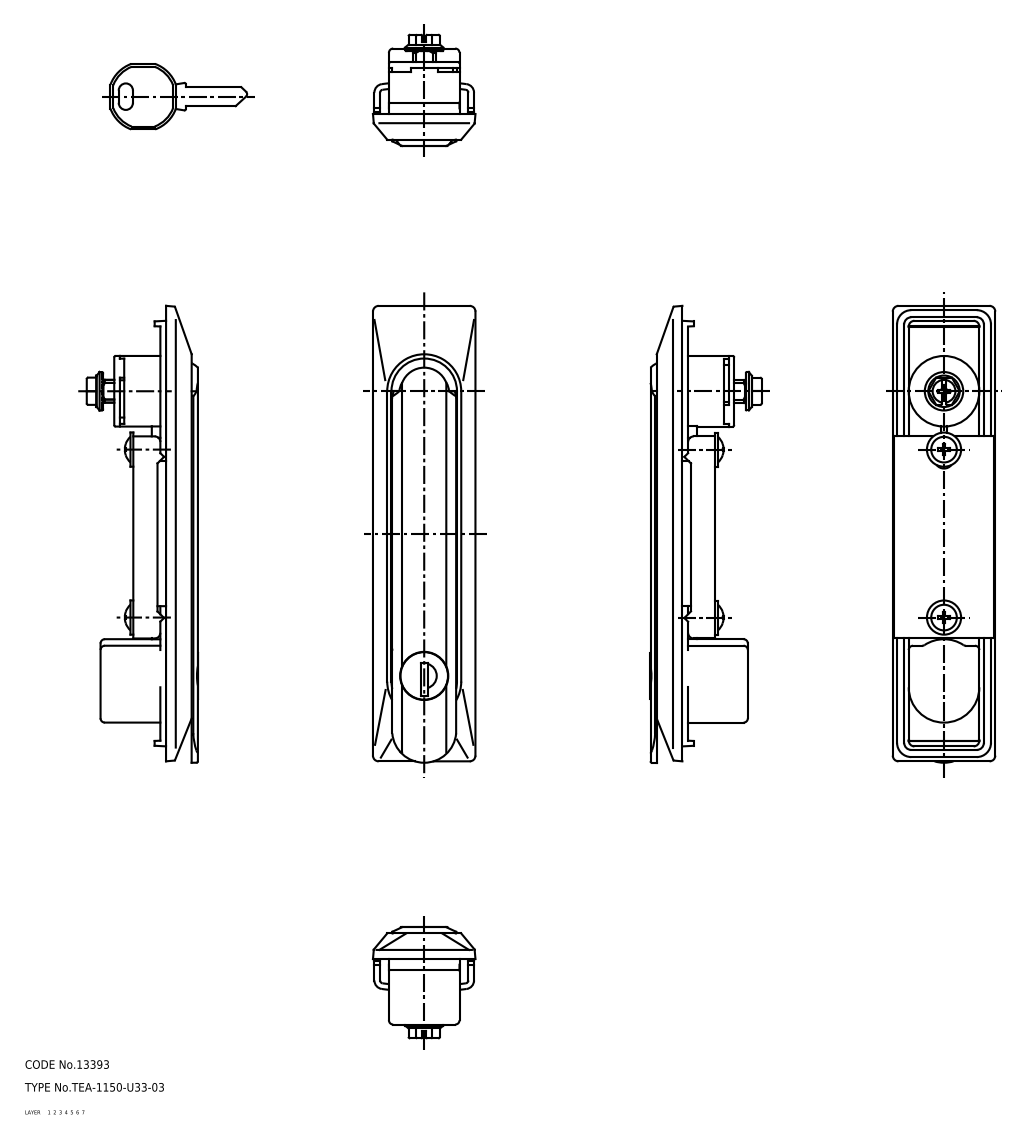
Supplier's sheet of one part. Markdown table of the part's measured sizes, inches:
| quantity | value |
| --- | --- |
| part name | 67136658; 67136671; 67136684; 67136697 (+3 more) |
| STEP written by | CADfix (AUTOMOTIVE_DESIGN) |
| units | inches |
| bodies | 7 solids, 515 faces (0 planar, 0 cylindrical, 515 other) |
| overall size | 6.319 × 4.366 × 1.417 |
| volume | 4.731 in³ |
| surface area | 70.57 in² |
